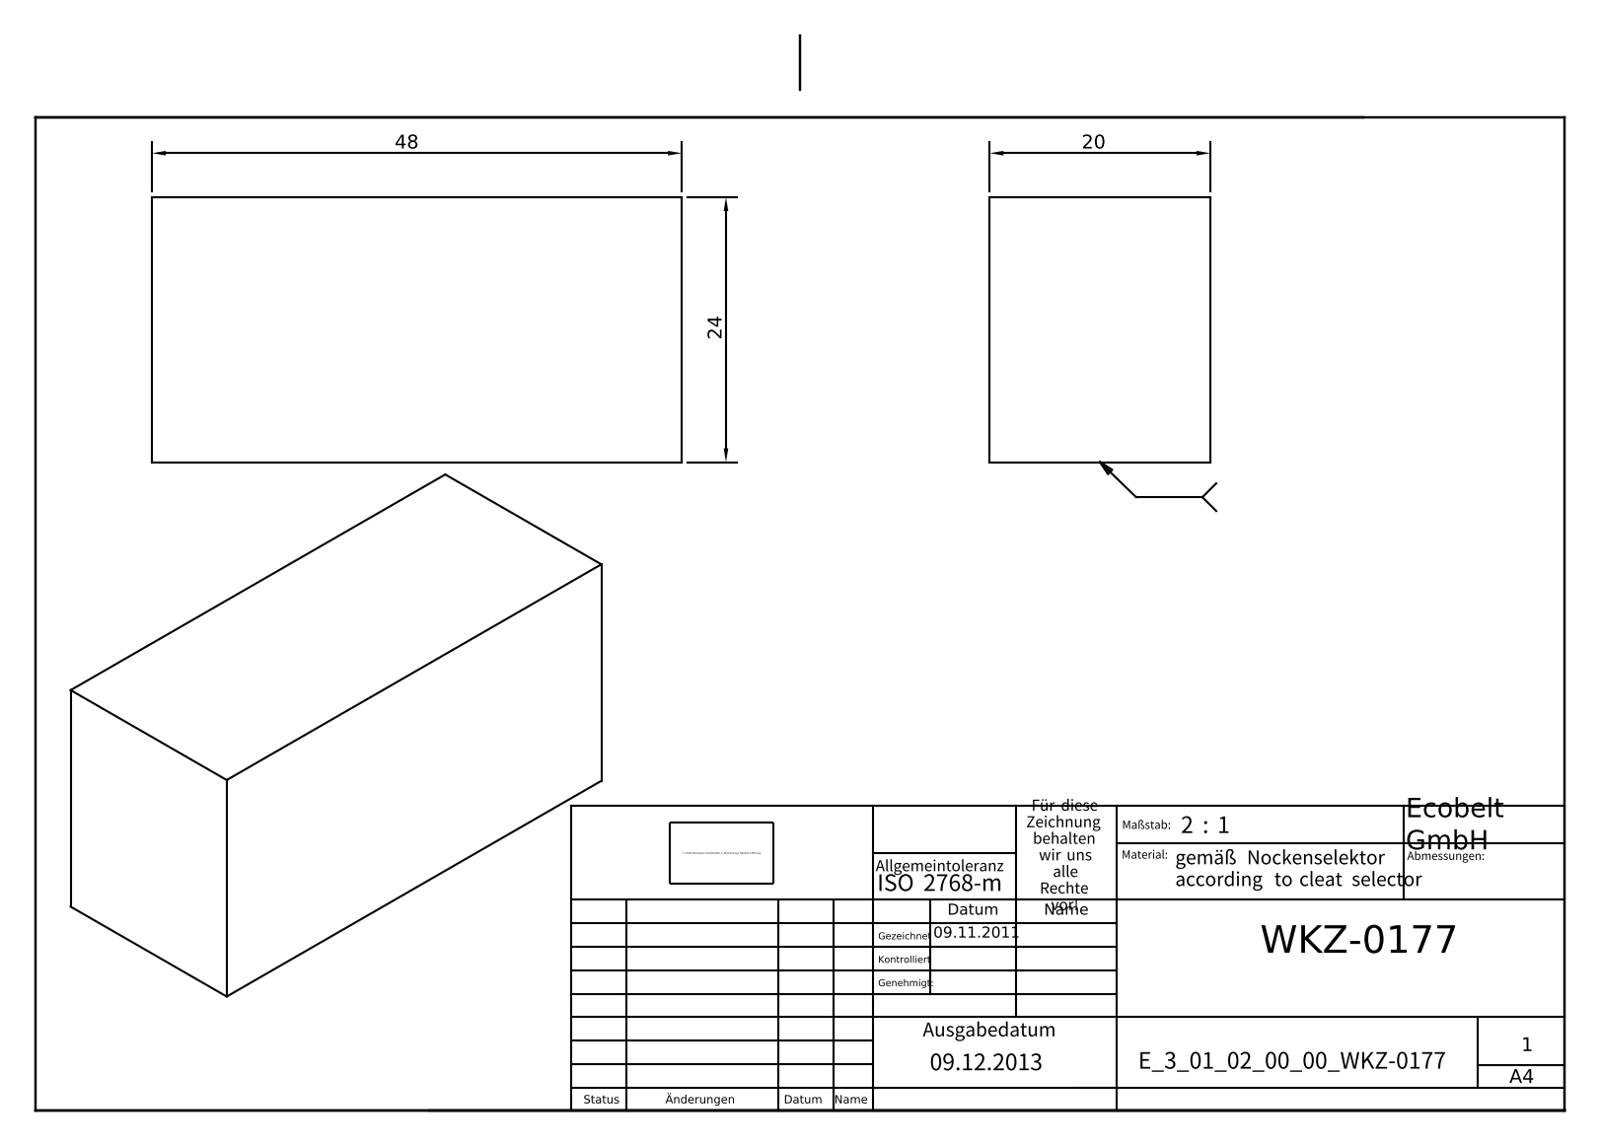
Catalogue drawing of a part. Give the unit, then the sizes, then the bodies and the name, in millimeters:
Units: millimetres
Overall size (bounding box): 48 × 24 × 20
Main face-to-face distances: 20, 24, 48
Volume: 23 040 mm³ · Surface area: 5 184 mm²
Bodies: 1 solid, 6 faces (6 planar, 0 cylindrical, 0 other)
Part name (STEP PRODUCT): E_3_01_02_00_00_WKZ-0177
STEP written by: Autodesk Inventor 2021 (AUTOMOTIVE_DESIGN)
